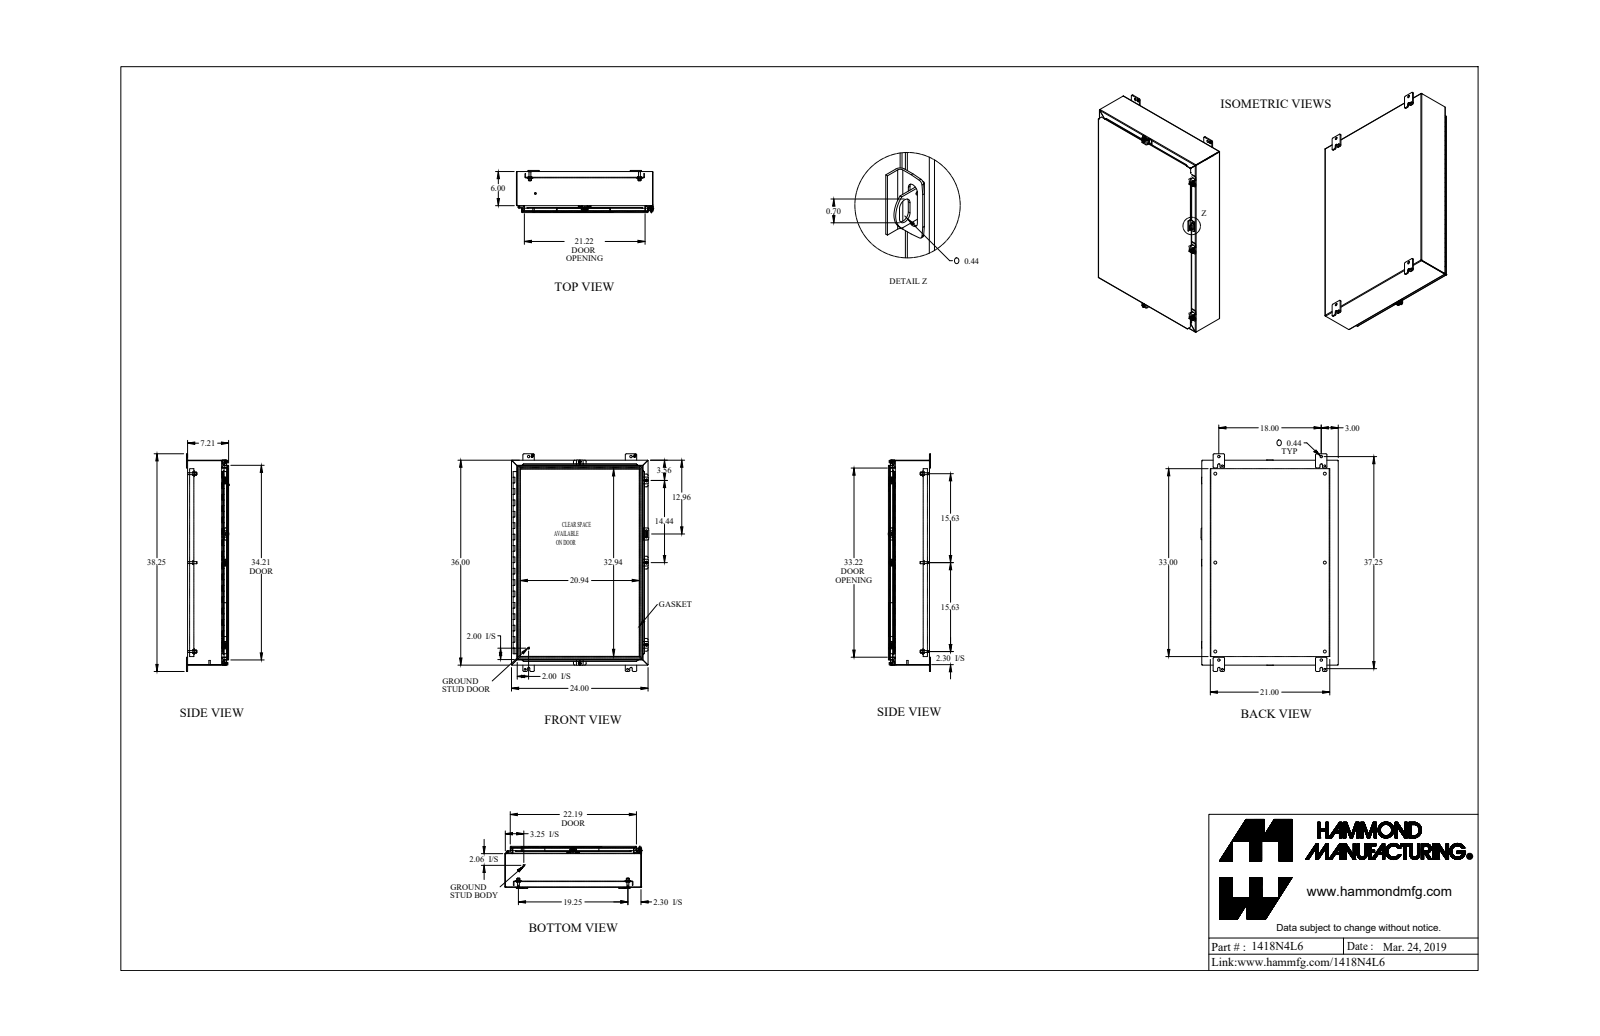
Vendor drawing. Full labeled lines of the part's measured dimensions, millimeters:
Part name (STEP PRODUCT): 1418N4L6_Default
STEP written by: SolidWorks 2019 (CONFIG_CONTROL_DESIGN)
Units: millimetres
Bodies: 49 solids, 1726 faces (1017 planar, 607 cylindrical, 102 other)
Overall size (bounding box): 971.6 × 612.8 × 188.9
Volume: 4 706 000 mm³ · Surface area: 4 814 000 mm²
Round holes (diameter × count): ⌀12.7 ×6, ⌀5.4 ×5, ⌀6.7 ×4, ⌀7.8 ×4, ⌀8 ×4, ⌀9.5 ×4, ⌀11.1 ×4, ⌀11.3 ×4, ⌀3.2 ×1, ⌀4.7 ×1, ⌀6.7 ×1, ⌀9.5 ×1
Round bosses / shafts (diameter × count): ⌀16.5 ×6, ⌀9.5 ×6, ⌀8.4 ×6, ⌀12.7 ×5, ⌀9.9 ×5, ⌀6.2 ×5, ⌀25.4 ×4, ⌀7.1 ×2
Partial cylindrical surfaces — rounded edges, fillets, slot ends (radius × count): R1.2 ×27, R3.6 ×27, R4.8 ×26, R0.9 ×24, R2.7 ×24, R6.4 ×24, R3.2 ×10, R3.6 ×10
Main face-to-face distances: 1.8, 1.8, 179.5, 181.3, 181.3, 183.1, 155.1, 153.3, 26.2, 28
Hole centre spacings: 489, 793.8, 932.3, 250.4, 250.4, 396.9, 396.9, 629.7
